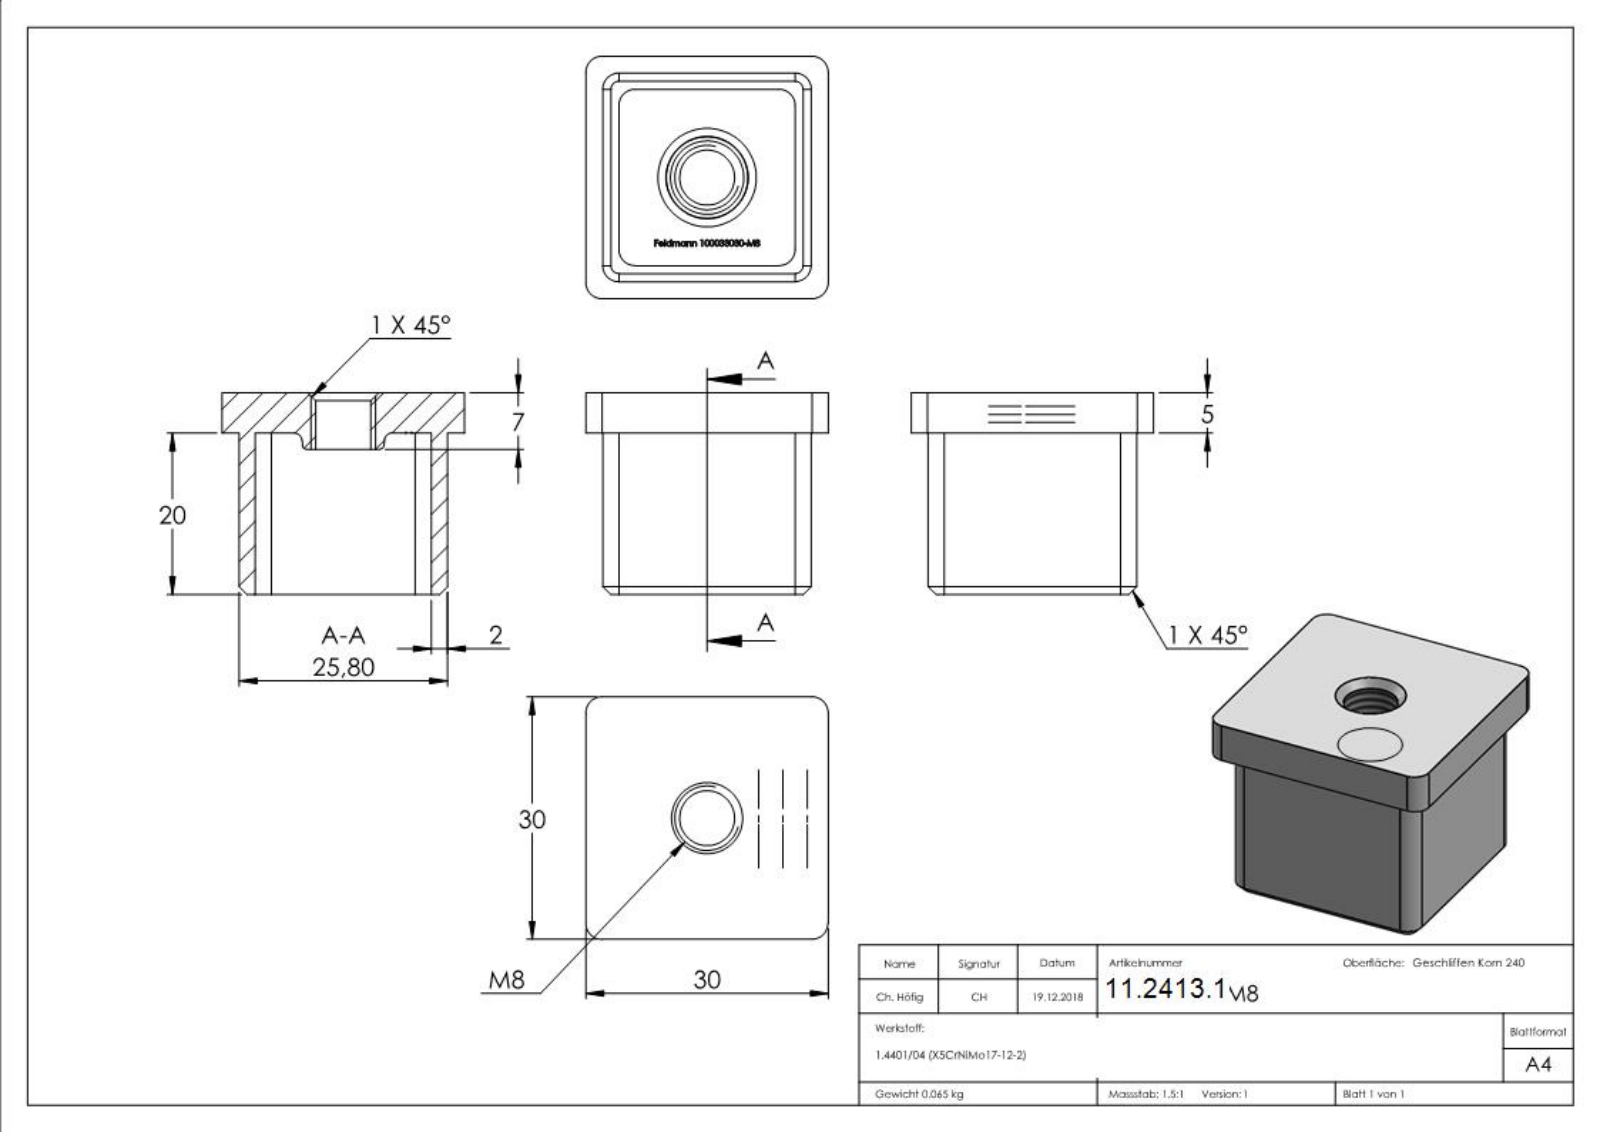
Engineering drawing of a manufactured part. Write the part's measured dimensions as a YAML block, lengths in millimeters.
part_name: "100033030-M8"
step_written_by: "SolidWorks 2015 (CONFIG_CONTROL_DESIGN)"
units: millimeters
bodies: {solids: 1, faces: 315, planar: 137, cylindrical: 14, other: 164}
overall_size: [30, 30, 25]
volume: 8143
surface_area: 6102
round_holes:
  - {diameter: 6.8, count: 1}
partial_cylinders:
  - {radius: 2, count: 12}
face_to_face_distances: [2, 23.8, 25.8, 21.8, 5, 2.1, 4.1, 25.9, 27.9, 30]
